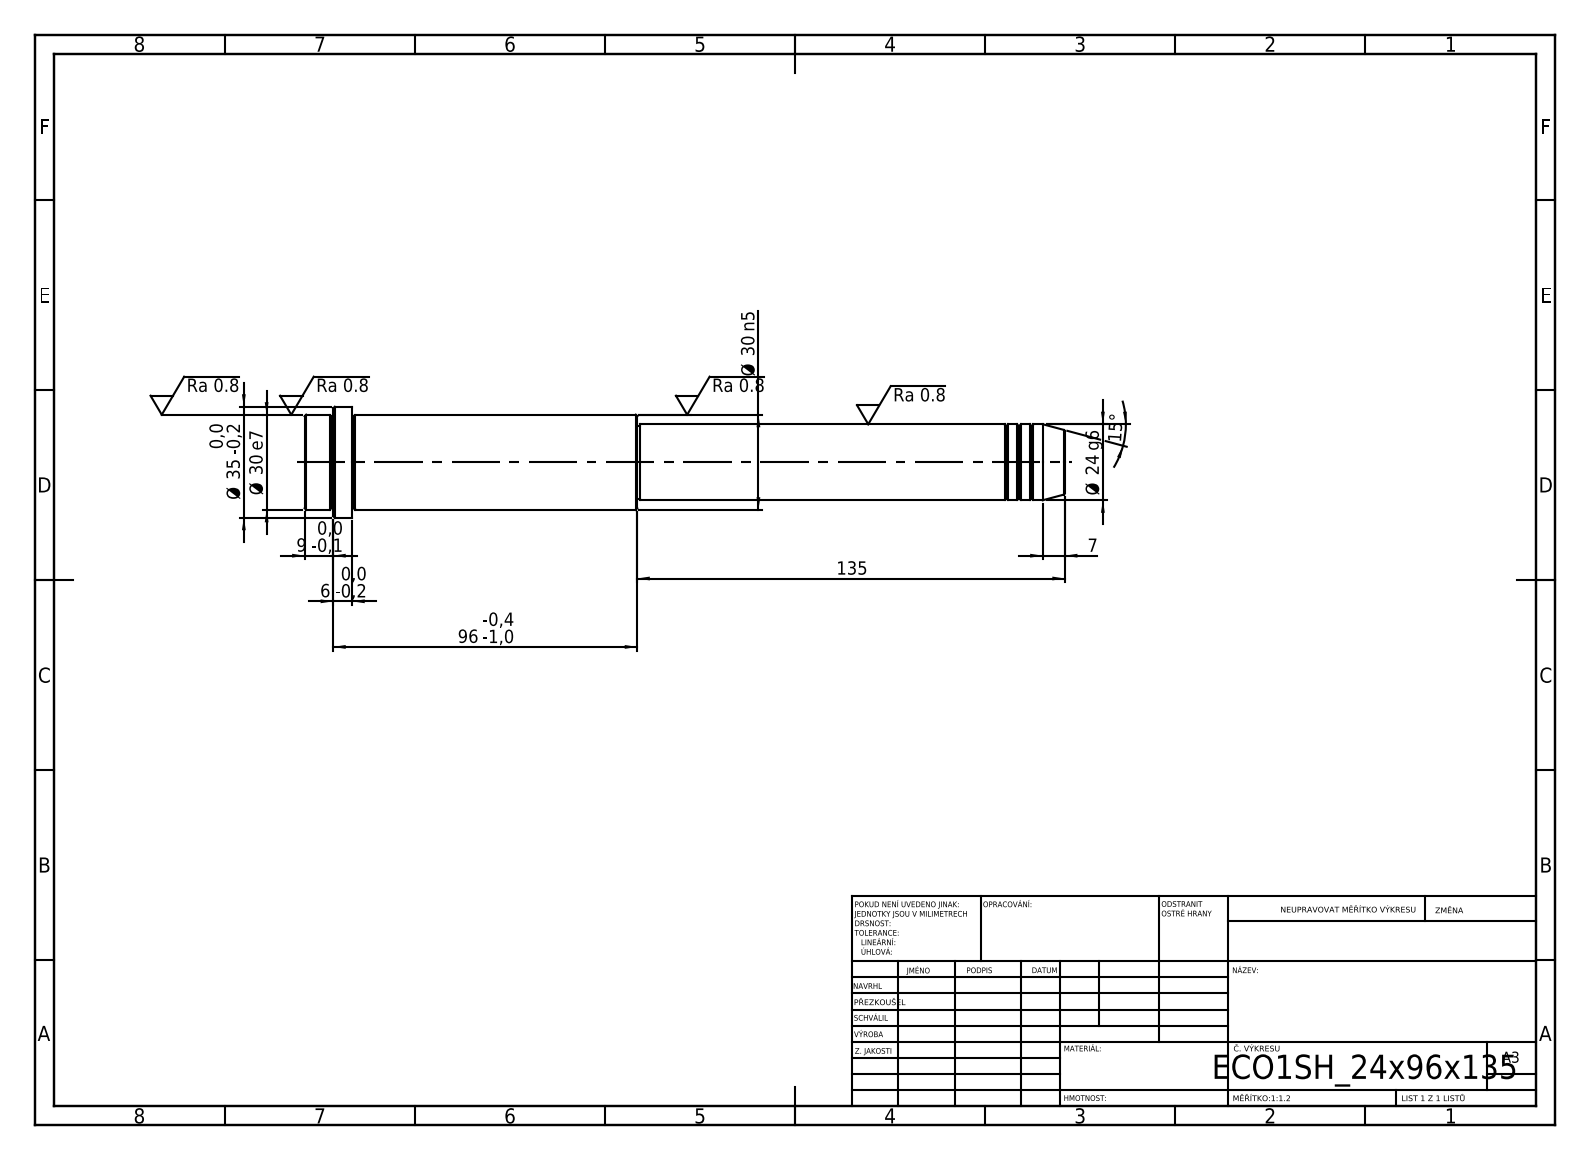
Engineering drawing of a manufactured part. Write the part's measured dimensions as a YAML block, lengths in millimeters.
step_written_by: "SolidWorks 2019 (CONFIG_CONTROL_DESIGN)"
units: millimeters
bodies: {solids: 1, faces: 52, planar: 6, cylindrical: 16, other: 30}
overall_size: [240, 35, 35]
volume: 136119
surface_area: 22135
round_bosses_or_shafts:
  - {diameter: 35, count: 1}
  - {diameter: 30, count: 1}
  - {diameter: 24, count: 1}
  - {diameter: 23, count: 1}
face_to_face_distances: [240, 225, 15, 135, 90, 105, 231, 96, 6, 9]
